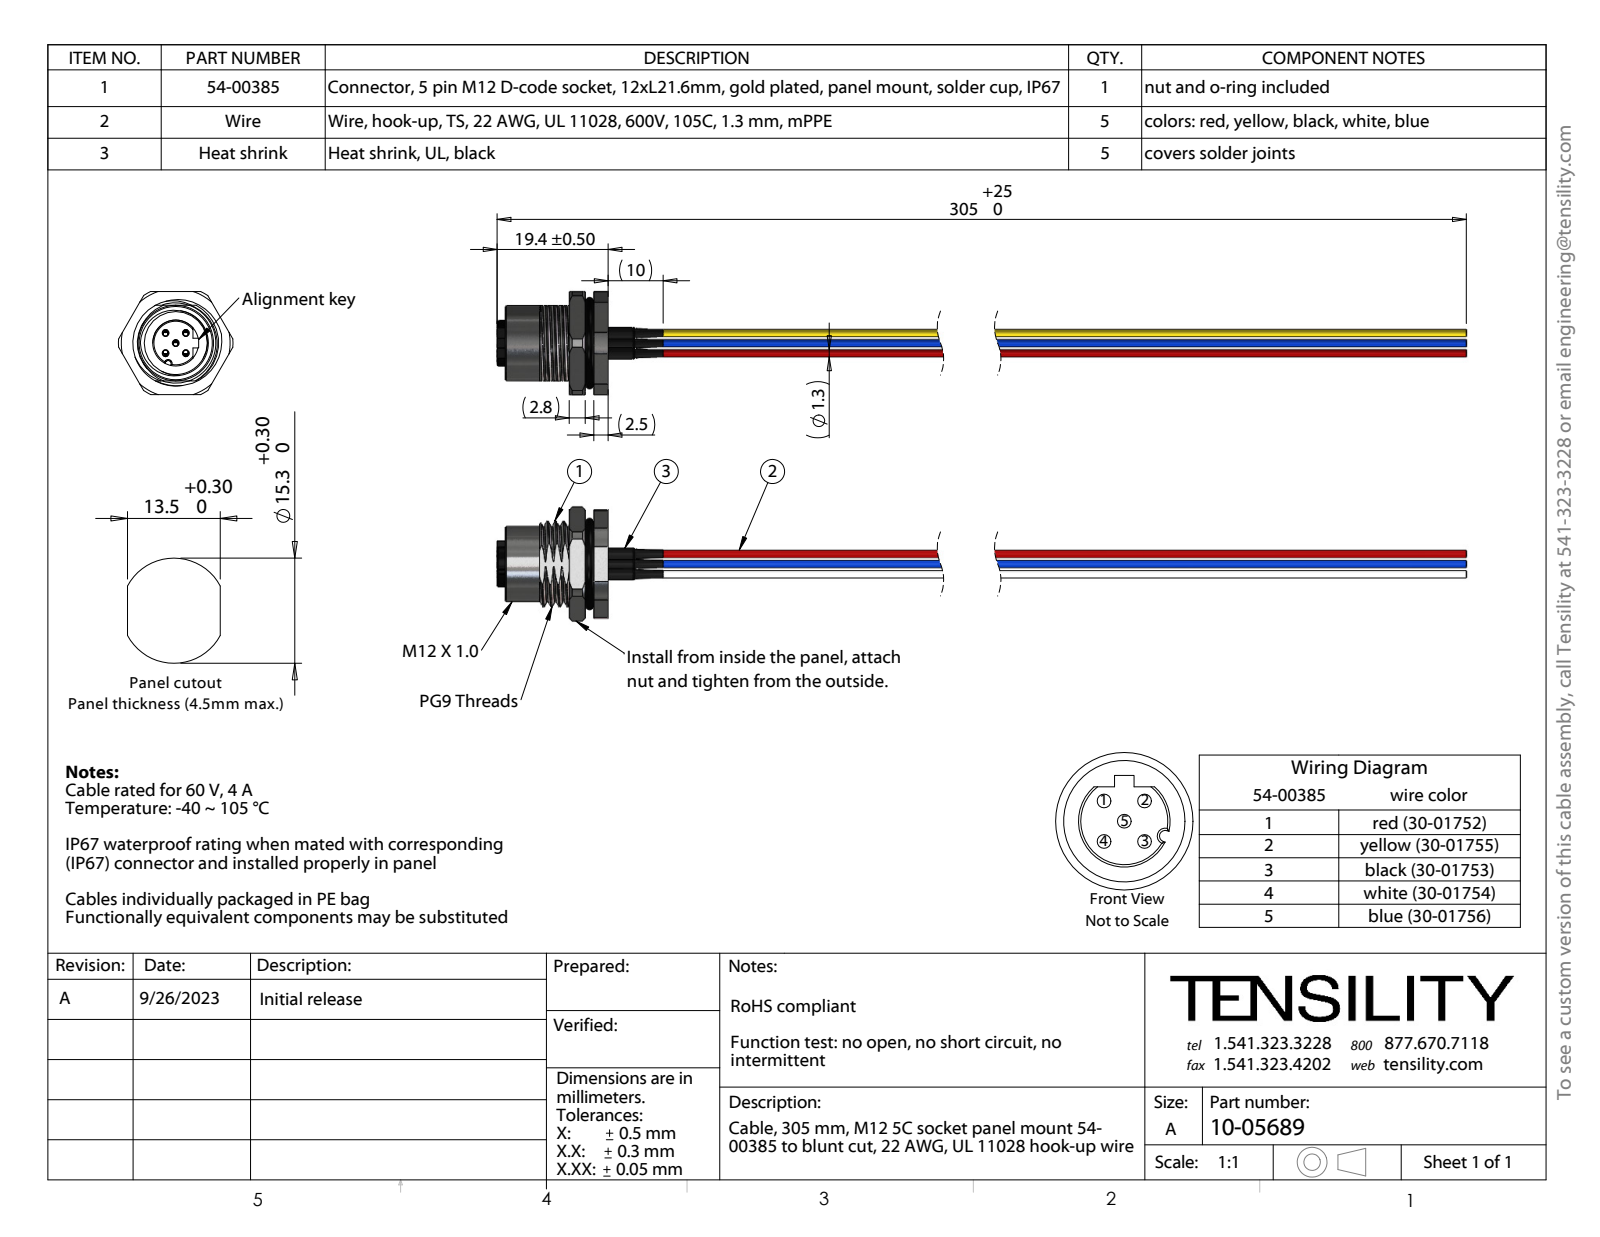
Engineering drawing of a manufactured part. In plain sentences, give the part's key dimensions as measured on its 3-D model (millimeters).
The part is named "30-01756_blunt cut; 30-01752_blunt cut; 54-00385-02; 54-00385-05 (+8 more)". Its 3-D file was written by "SolidWorks 2021 (AUTOMOTIVE_DESIGN)". It is 106 solids with 1222 faces: 370 planar, 576 cylindrical and 276 other. Overall it measures 169 by 20 by 18 millimeters. Its volume is 4 005 cubic millimeters and its surface area 21 851 square millimeters. Round holes: 5 of diameter 1.1, 5 of diameter 1.2, 1 of diameter 9, 1 of diameter 11, 1 of diameter 14. Round bosses or shafts: 5 of diameter 2, 5 of diameter 1.6, 5 of diameter 1.5, 5 of diameter 1.3, 1 of diameter 13.2, 1 of diameter 12, 1 of diameter 10.6. Partial cylindrical surfaces (rounded edges, fillets, slot ends): 10 of radius 0.1, 8 of radius 0.4, 2 of radius 0.2, 1 of radius 0.5, 1 of radius 4, 1 of radius 7.5, 1 of radius 9.5, 1 of radius 10. The main face-to-face distances are 2.5, 0.4, 2.1, 18, 1.4, 3.6, 4, 6.4, 1.5, 4.3. The hole center spacings are 0.48, 0.32, 3.54, 5, 0.31, 0.37, 4.89, 0.53.
